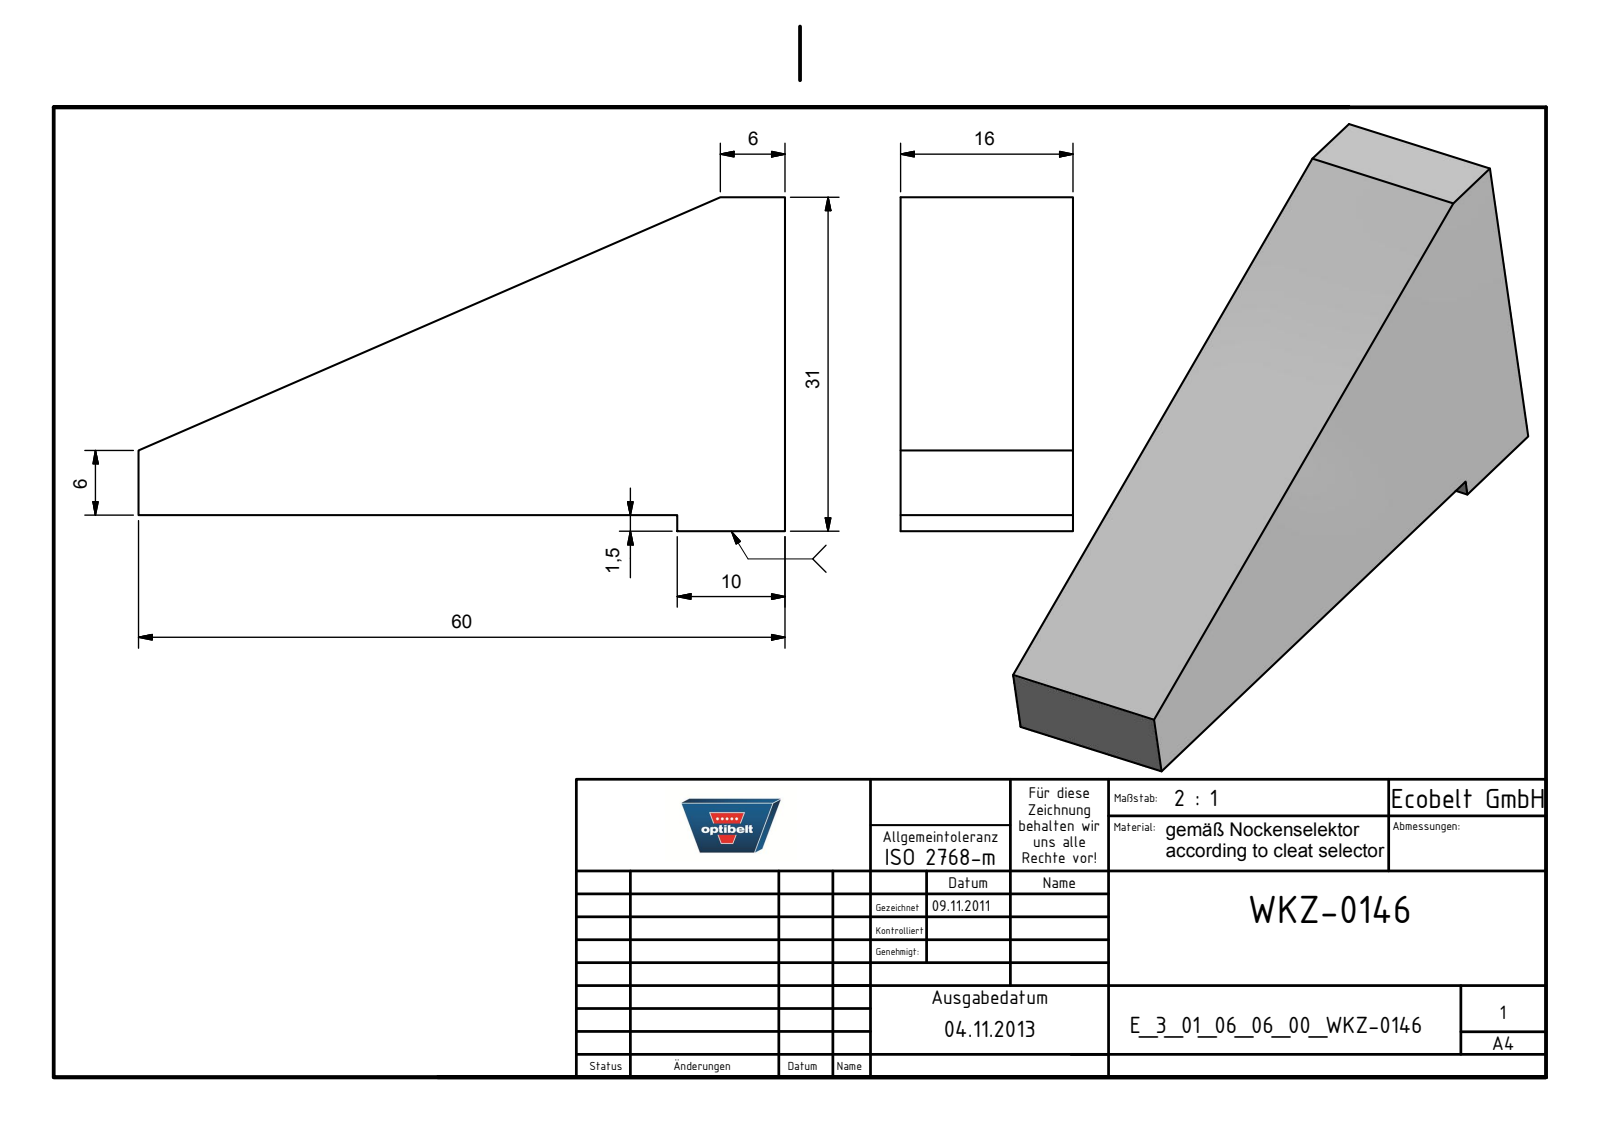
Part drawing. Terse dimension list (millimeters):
name: E_3_01_06_06_00_WKZ-0146
written by: Autodesk Inventor 2025 (AUTOMOTIVE_DESIGN)
unit: mm
bodies: 1 solid, 9 faces (9 planar, 0 cylindrical, 0 other)
size: 60 × 31 × 16
volume: 18 408 mm³; area: 4 915 mm²
face distances: 16, 1.5, 60, 31, 29.5, 50, 10
